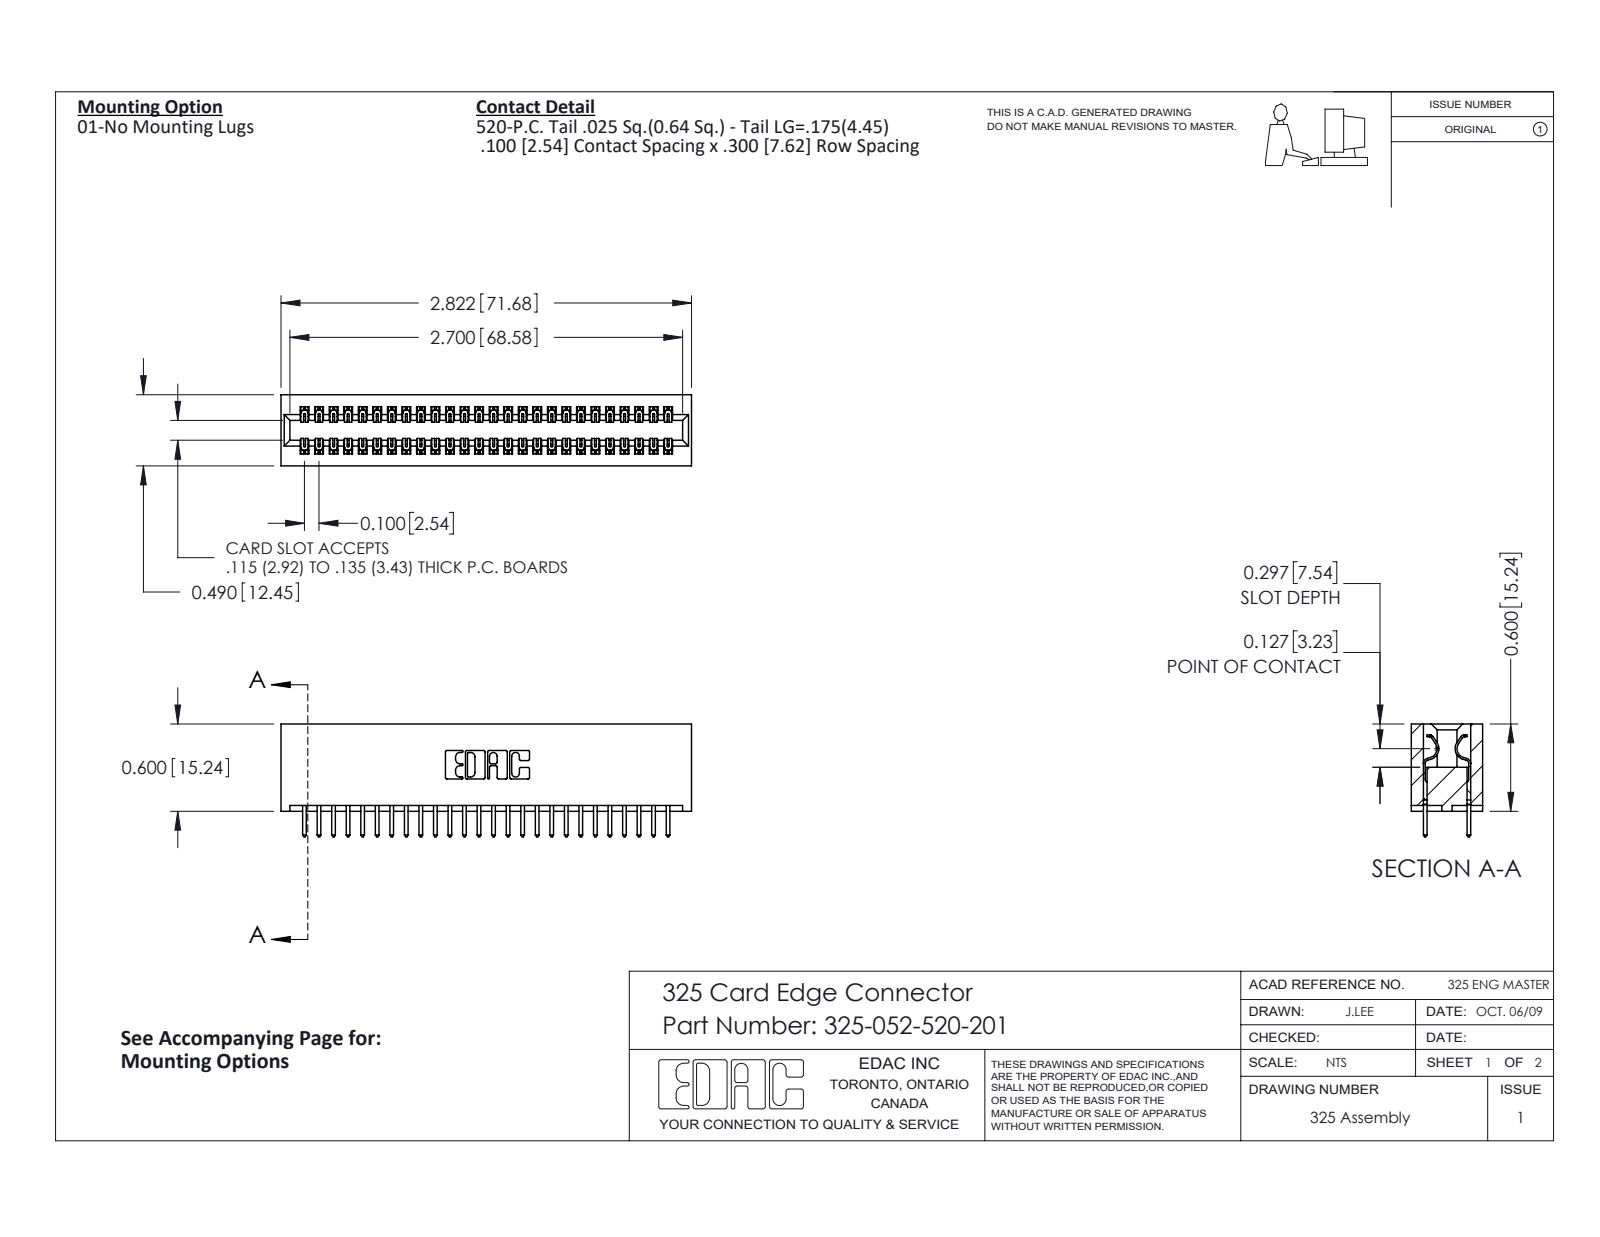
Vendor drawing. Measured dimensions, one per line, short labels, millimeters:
name: 325 Part_Lugless; 325-052-520-201; 325-292-001_325-293-120
written by: SolidWorks 2016 (CONFIG_CONTROL_DESIGN)
unit: mm
bodies: 53 solids, 2810 faces (1938 planar, 872 cylindrical, 0 other)
size: 71.7 × 19.7 × 12.4
volume: 9 700 mm³; area: 11 930 mm²
rounds: 78× R0.2, 52× R0.3, 22× R0.3, 6× R0.2, 6× R0.8, 3× R0.7, 2× R0.4, 2× R0.6
face distances: 2.1, 10.3, 7.6, 12.4, 2.7, 9.7, 0.6, 8.3, 7, 14.2
